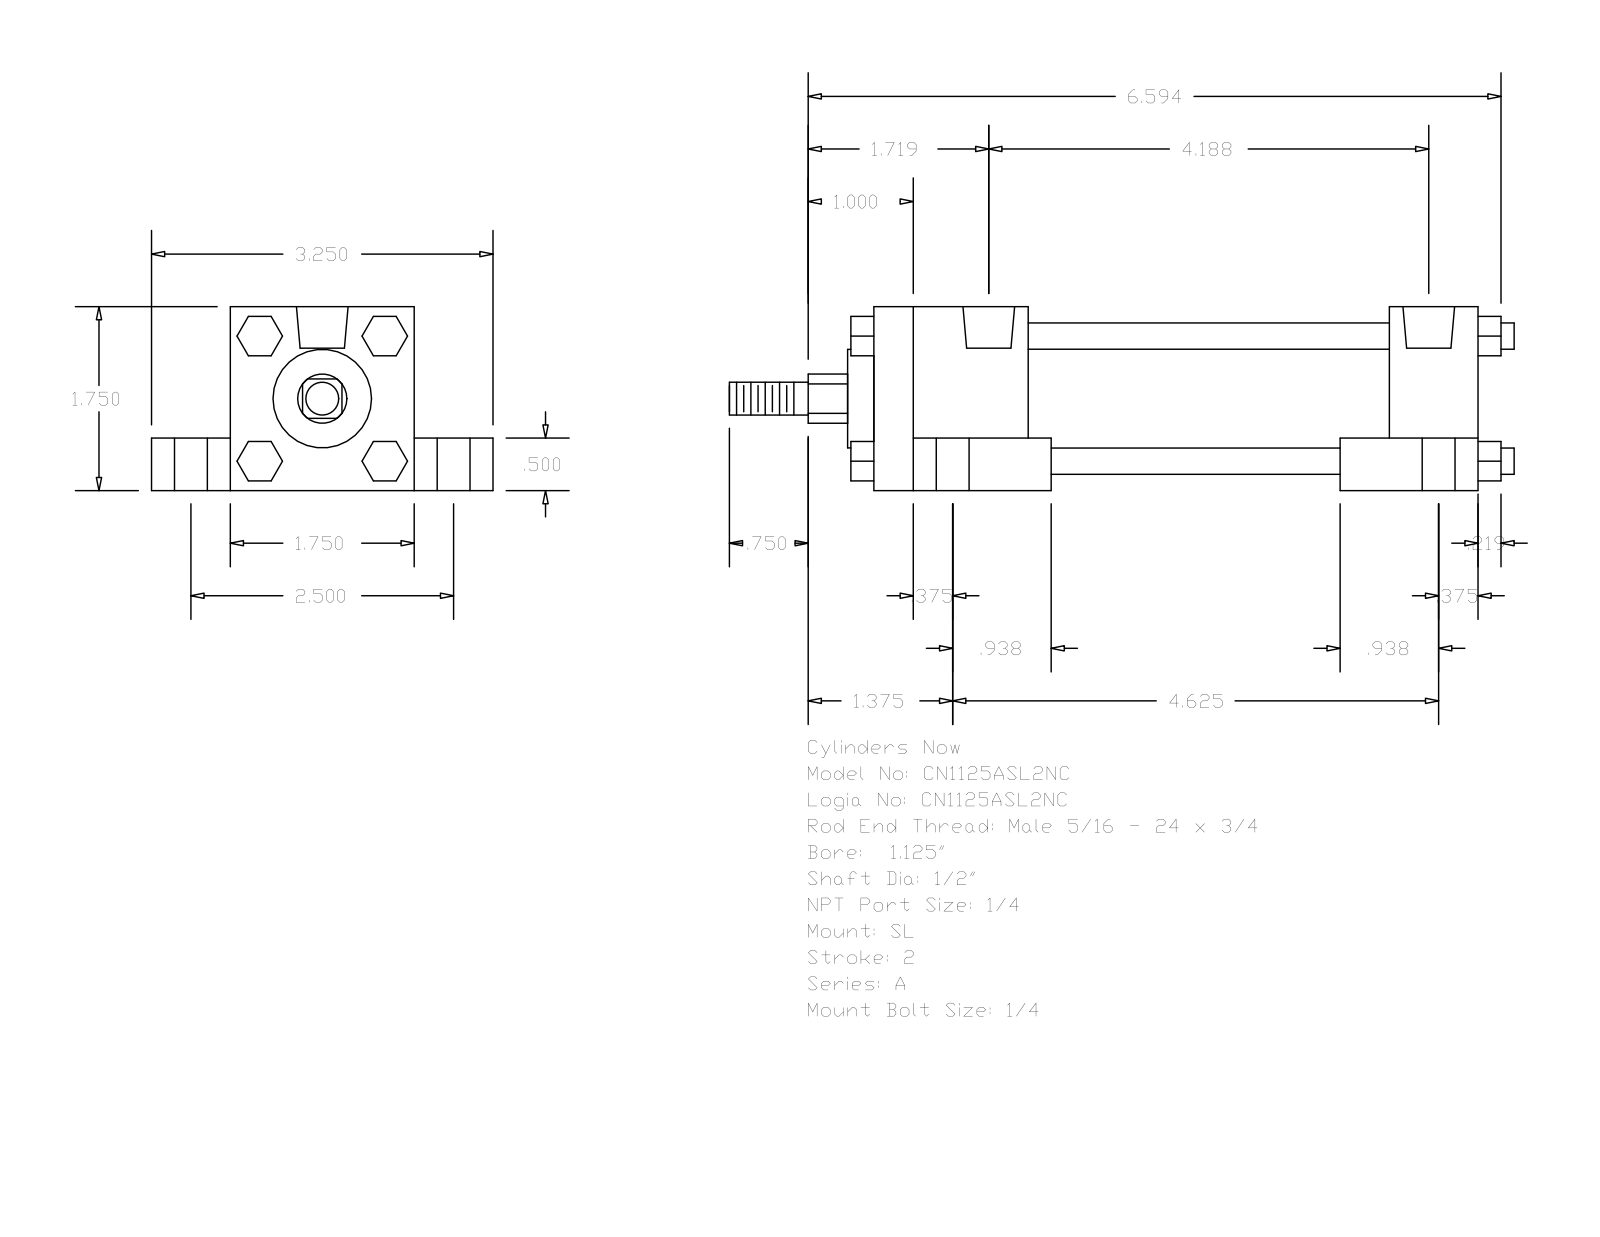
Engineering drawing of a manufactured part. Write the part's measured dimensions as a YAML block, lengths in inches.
part_name: "A_SL__0112_0.5"
step_written_by: "GSSL Pune (CONFIG_CONTROL_DESIGN)"
units: inches
bodies: {solids: 0, faces: 150, planar: 114, cylindrical: 36, other: 0}
overall_size: [7.469, 3.25, 1.75]
round_holes:
  - {diameter: 0.219, count: 4}
  - {diameter: 0.313, count: 4}
  - {diameter: 0.563, count: 4}
  - {diameter: 0.492, count: 2}
round_bosses_or_shafts:
  - {diameter: 0.25, count: 4}
  - {diameter: 1.255, count: 1}
  - {diameter: 0.937, count: 1}
  - {diameter: 0.5, count: 1}
  - {diameter: 0.313, count: 1}
partial_cylinders:
  - {radius: 0.234, count: 1}
face_to_face_distances: [1.75, 1.25, 0.5, 0.75, 2.5, 5.75, 4.906, 0.844, 1.469, 3.437]
hole_center_spacings: [1.254, 1.26, 1.296, 1.315, 2.5, 4.063, 4.4, 4.46]
